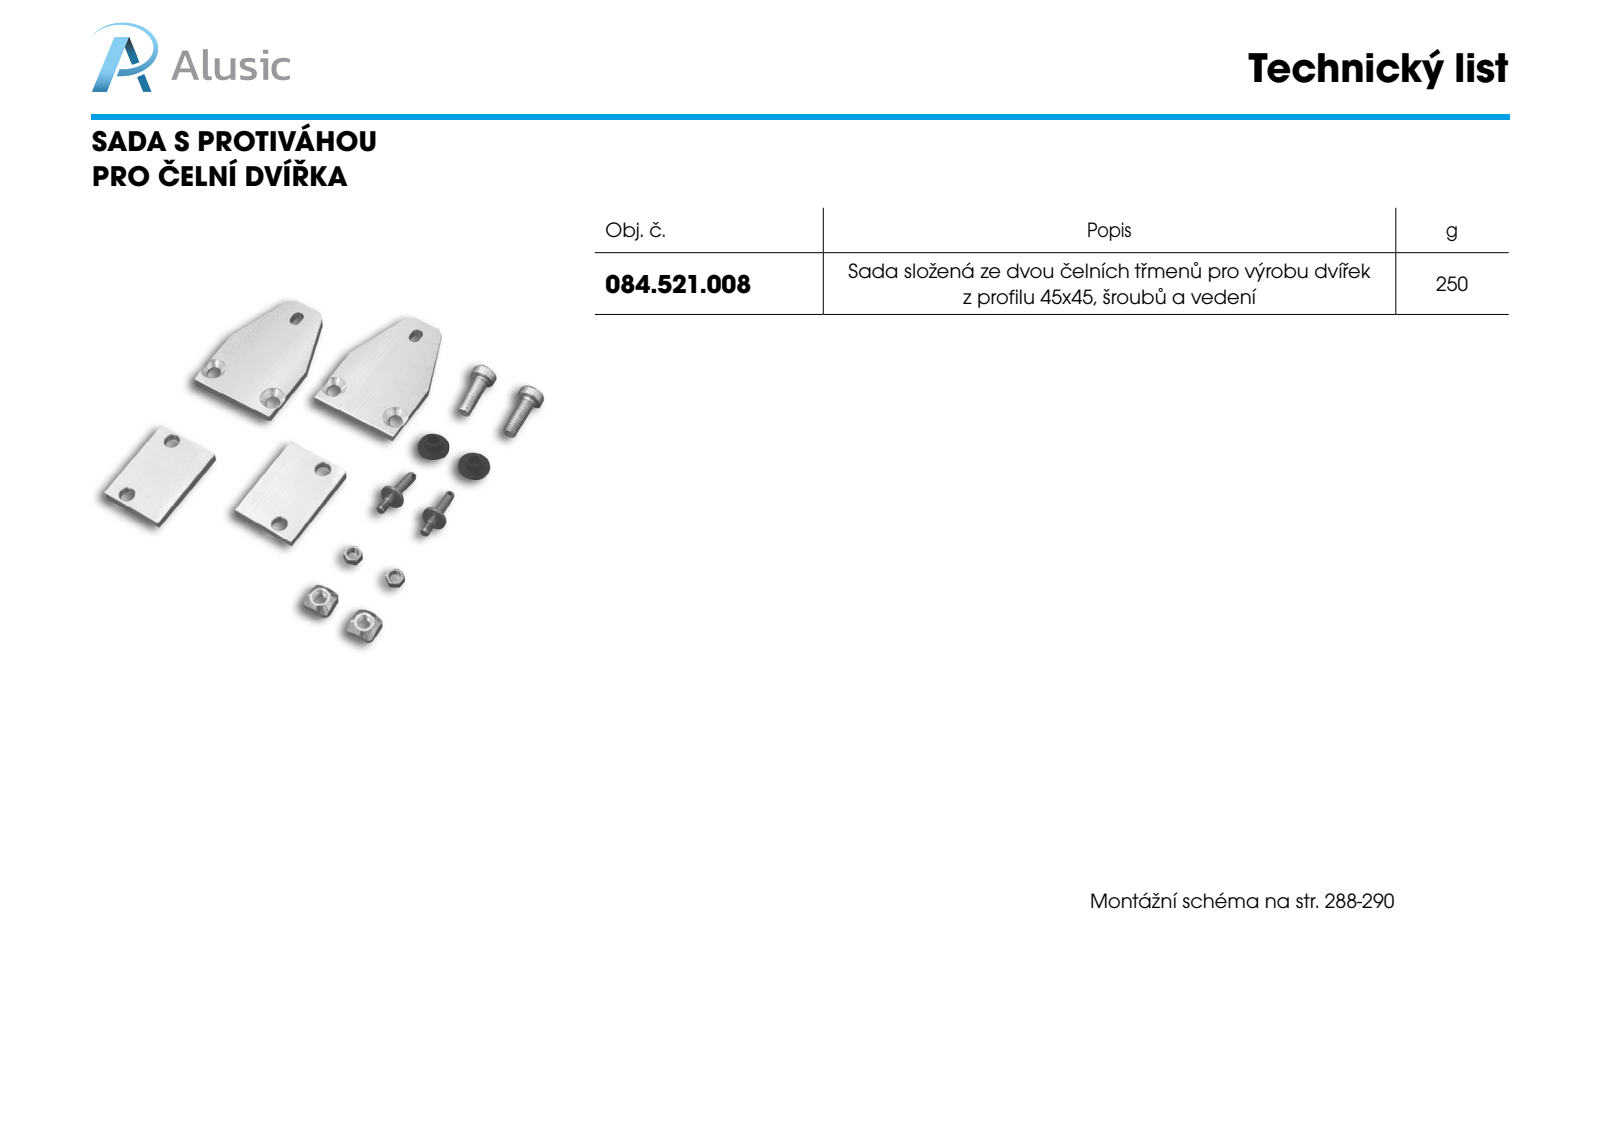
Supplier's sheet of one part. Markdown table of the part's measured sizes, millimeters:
| quantity | value |
| --- | --- |
| part name | 084.521.008; 084.521.105; 084.521.108; 084.302.000 DADI ALUSIC 13x13-1_084.302.003 (+4 more) |
| STEP written by | SolidWorks 2016 (CONFIG_CONTROL_DESIGN) |
| units | millimeters |
| bodies | 9 solids, 486 faces (70 planar, 150 cylindrical, 266 other) |
| overall size | 70.75 × 48 × 35 |
| volume | 23 517 mm³ |
| surface area | 14 807 mm² |
| round holes (diameter × count) | 4.2 × 3, 6.5 × 2, 7 × 2, 2 × 1, 5.1 × 1 |
| round bosses / shafts (diameter × count) | 11.34 × 2, 6 × 2, 15 × 1, 12 × 1, 8 × 1, 5 × 1, 4.5 × 1 |
| partial cylindrical surfaces (radius × count) | 2.75 × 2, 5 × 1, 15 × 1 |
| main face-to-face distances | 5, 10, 1.5, 3.5, 4, 45, 9, 14, 6.5, 7.5 |
| hole center spacings | 2.5, 32.5, 55.32, 56.05, 30, 35 |
